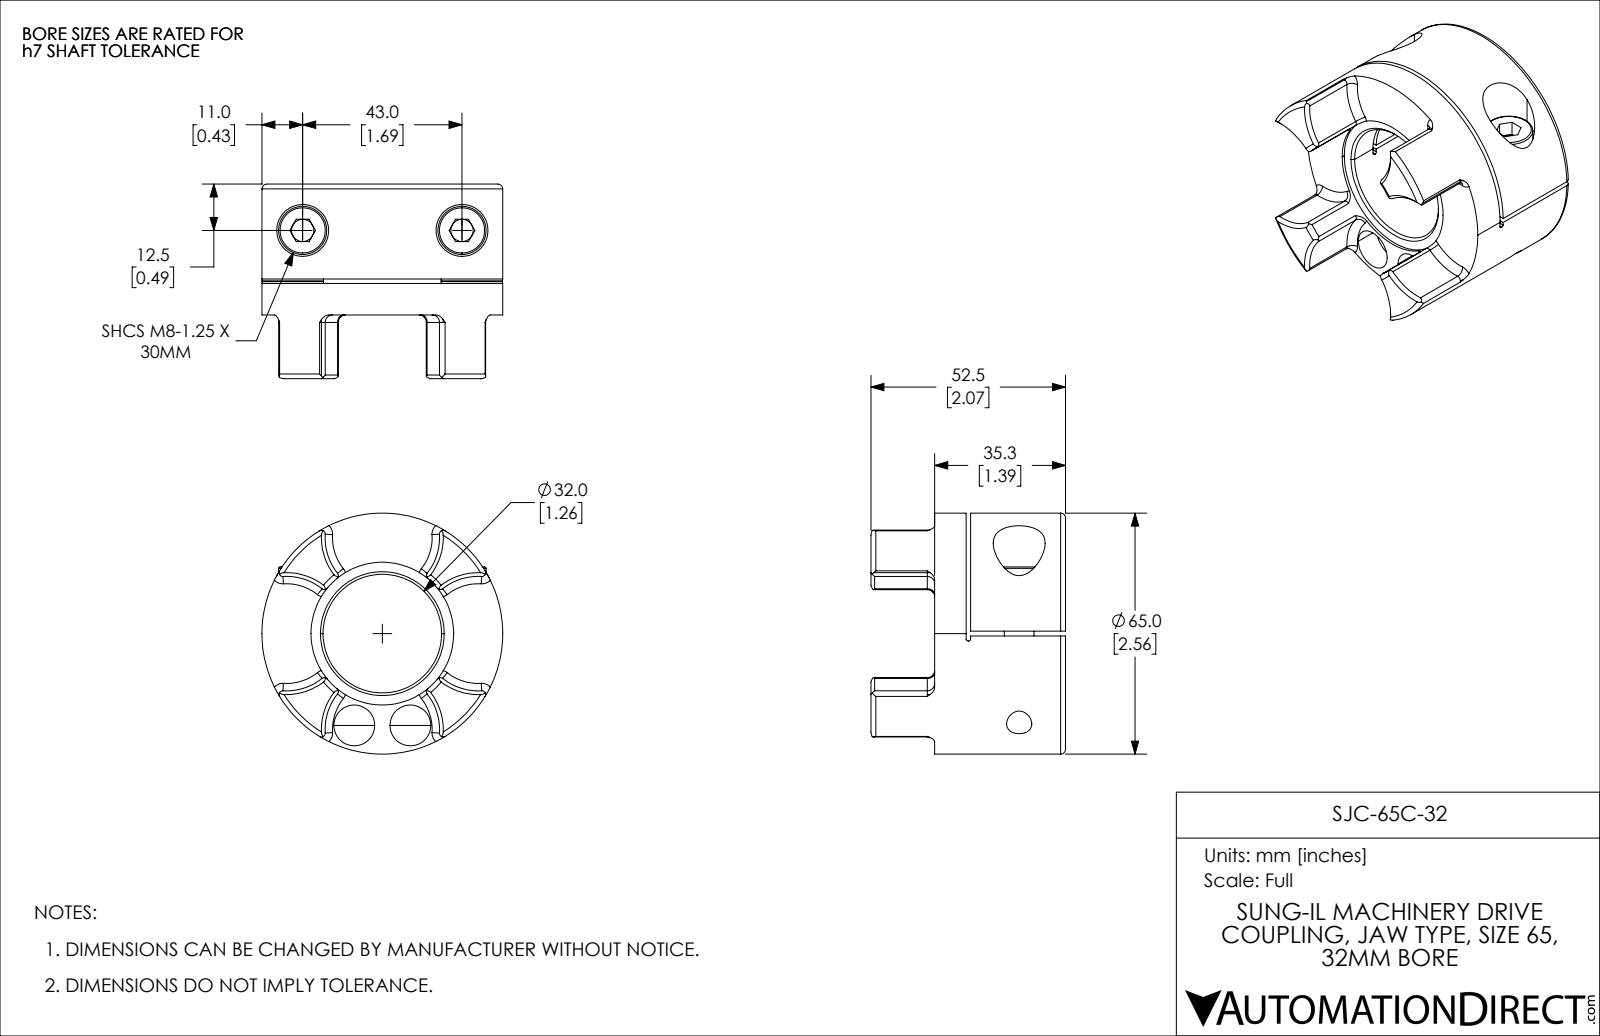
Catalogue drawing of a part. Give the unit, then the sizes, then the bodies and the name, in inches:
Units: inches
Overall size (bounding box): 2.559 × 2.559 × 2.067
Round holes (diameter × count): ⌀0.236 ×2, ⌀0.268 ×2, ⌀0.335 ×2, ⌀0.433 ×2, ⌀0.551 ×2, ⌀1.26 ×1, ⌀1.516 ×1
Round bosses / shafts (diameter × count): ⌀0.512 ×2, ⌀0.315 ×2, ⌀2.559 ×1
Partial cylindrical surfaces — rounded edges, fillets, slot ends (radius × count): R0.039 ×16, R0.608 ×4, R0.02 ×2
Main face-to-face distances: 1.055, 0.047, 1.008, 0.335, 0.382, 1.39, 0.051, 0.677, 1.012, 1.059
Hole centre spacings: 1.019, 0.596, 1.693
Volume: 5.562 in³ · Surface area: 43.81 in²
Bodies: 4 solids, 207 faces (53 planar, 72 cylindrical, 82 other)
Part name (STEP PRODUCT): SJC-65C-32
STEP written by: SolidWorks 2021 (CONFIG_CONTROL_DESIGN)
